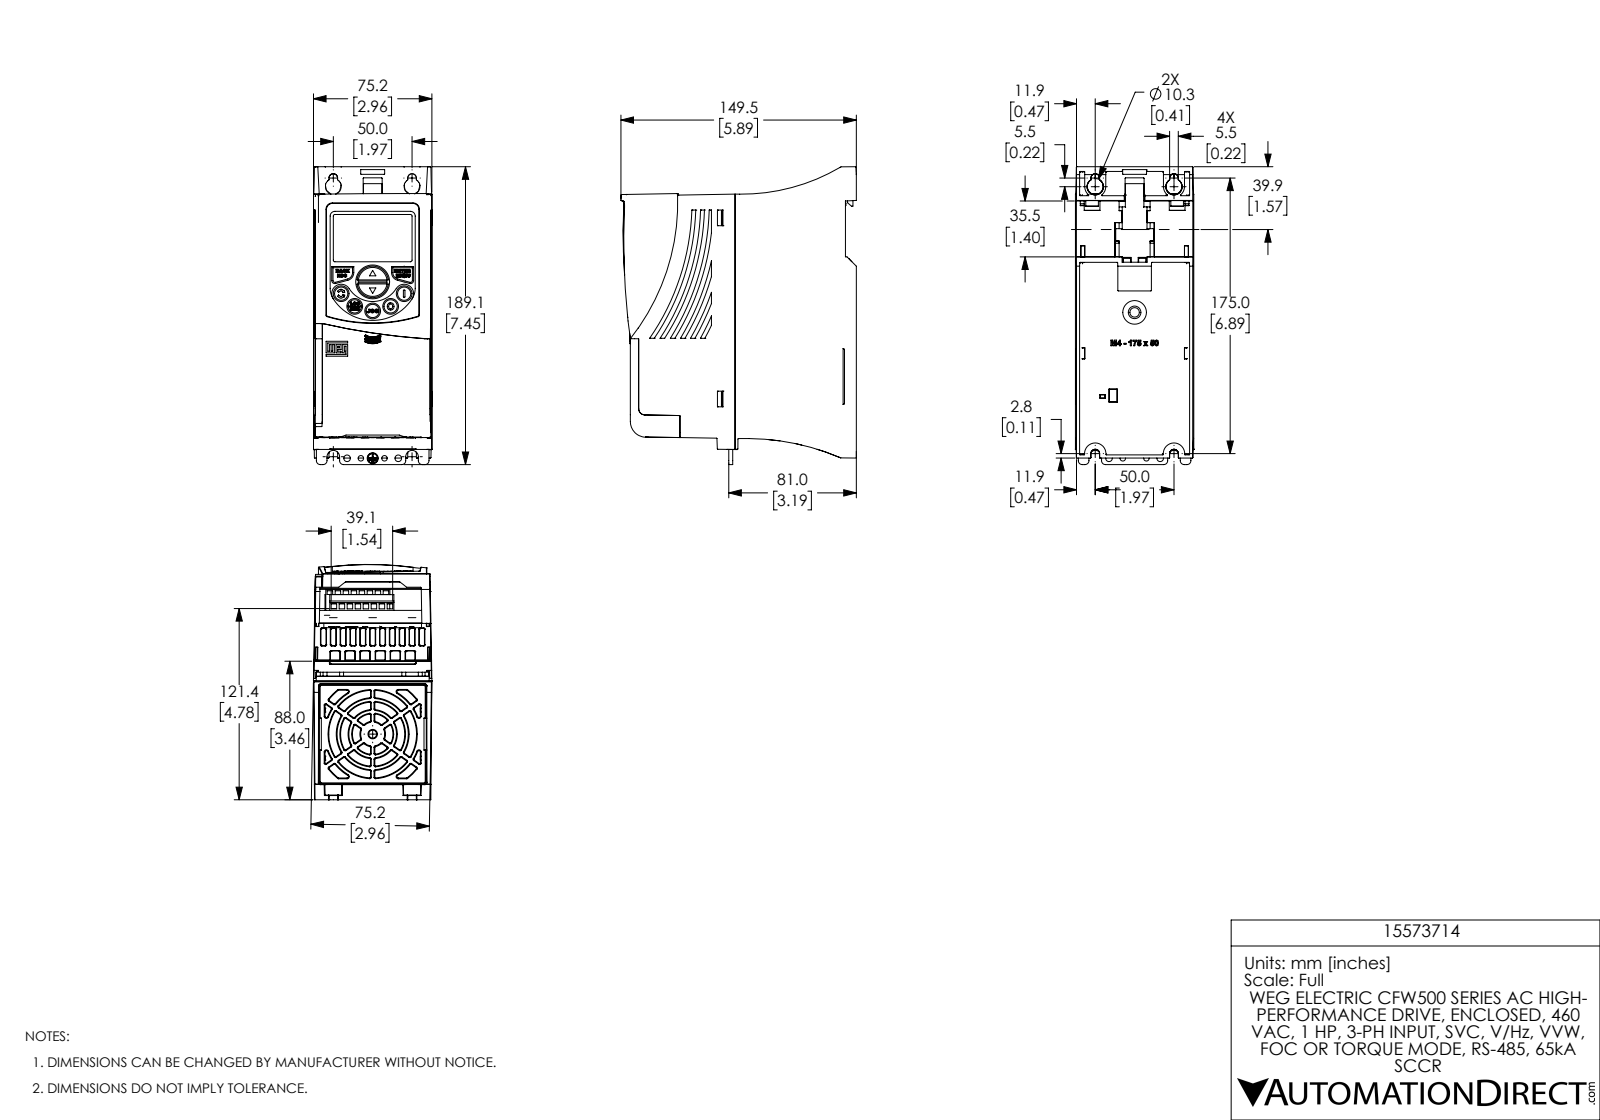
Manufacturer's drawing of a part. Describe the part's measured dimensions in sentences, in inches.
The part is named "CFW50X_FRAME_A_NEMA1_PAR R1b red1 ext2 Bclr 2dB". Its 3-D file was written by "SolidWorks 2017 (AUTOMOTIVE_DESIGN)". It is 14 solids with 3862 faces: 1785 planar, 686 cylindrical and 1391 other. Overall it measures 7.447 by 5.885 by 2.962 inches. Its volume is 93.03 cubic inches and its surface area 341.3 square inches. Round holes: 3 of diameter 0.394, 2 of diameter 0.098, 2 of diameter 0.138, 2 of diameter 0.165, 2 of diameter 0.386, 1 of diameter 0.787, 1 of diameter 0.846. Round bosses or shafts: 2 of diameter 0.394. Partial cylindrical surfaces (rounded edges, fillets, slot ends): 244 of radius 0.012, 87 of radius 0.008, 35 of radius 0.02, 24 of radius 0.039, 6 of radius 0.098, 3 of radius 0.157, 3 of radius 0.197, 2 of radius 0.033. The main face-to-face distances are 0.122, 0.117, 0.059, 0.079, 0.02, 1.053, 5.276, 5.398, 0.063, 5.169. The hole center spacings are 0.898, 0.344, 0.463, 0.464, 0.759, 0.764, 0.841, 0.935.
